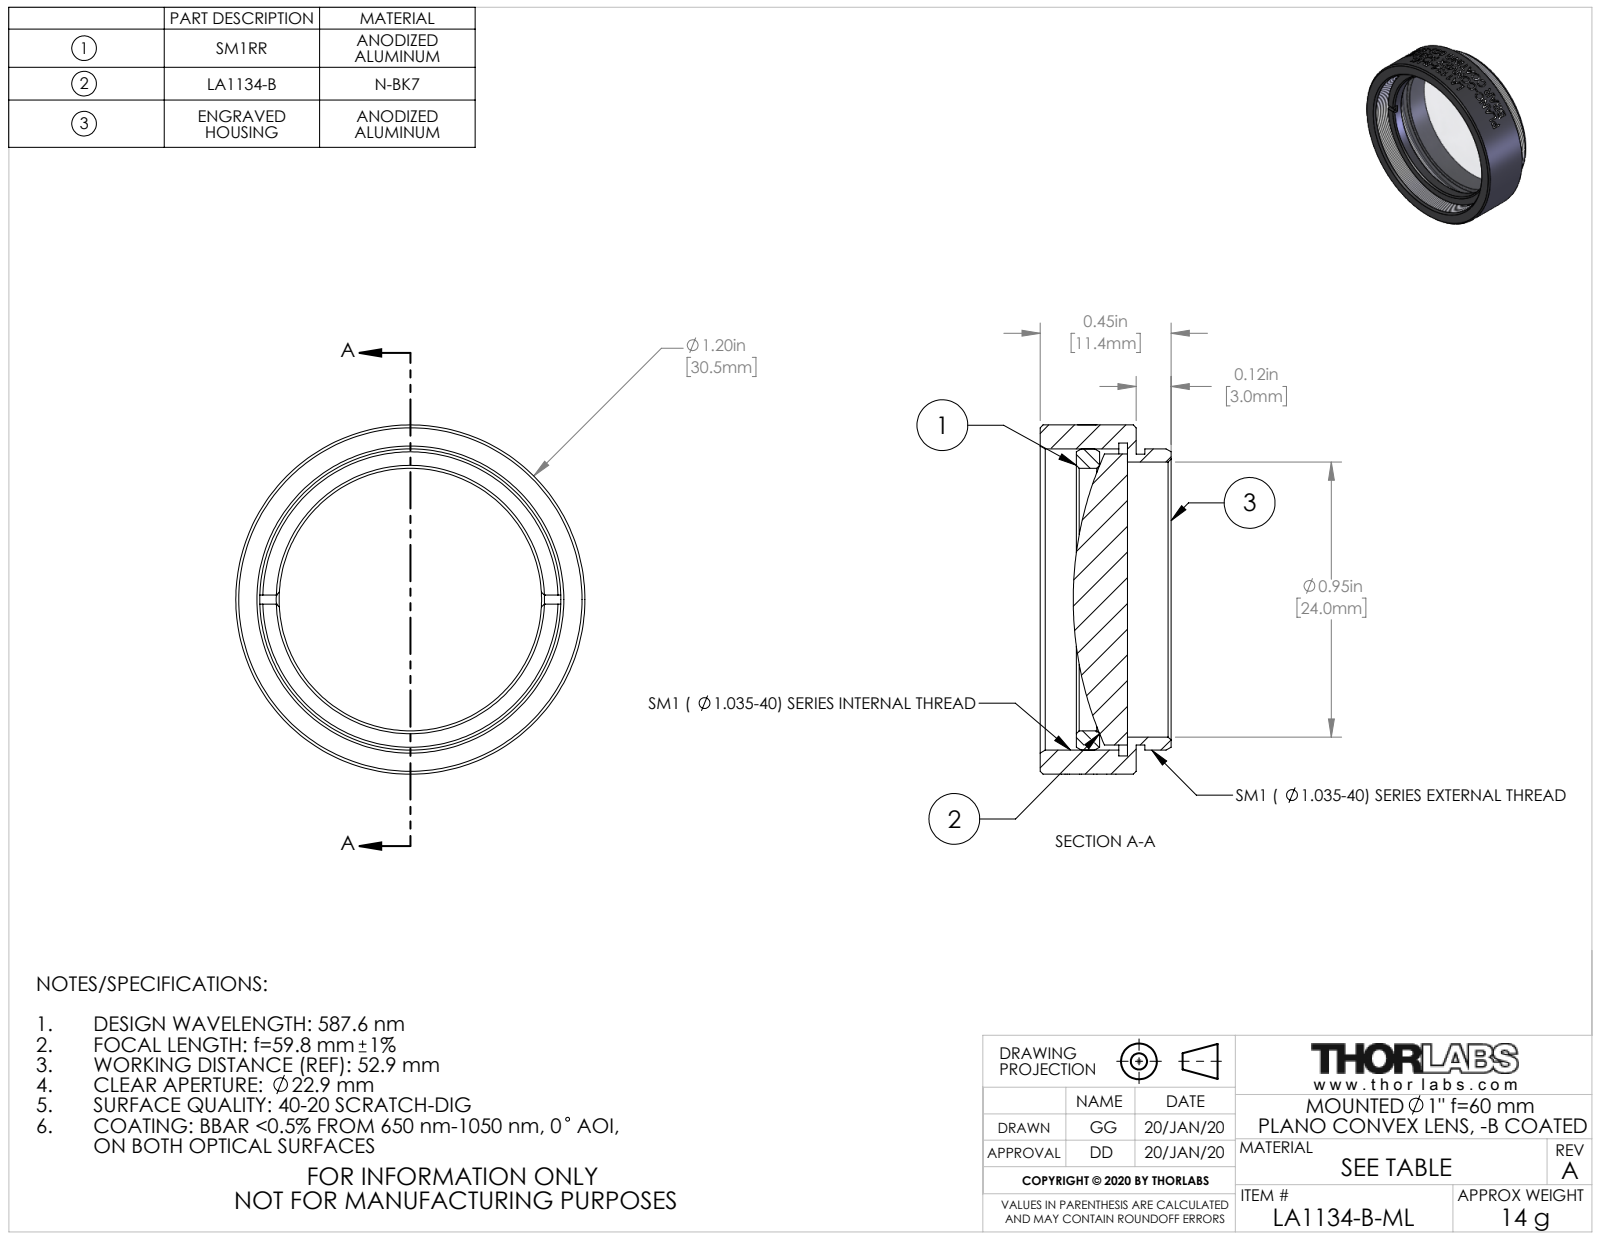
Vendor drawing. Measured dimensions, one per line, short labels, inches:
name: TTN203743-E0W
written by: SolidWorks 2018 (CONFIG_CONTROL_DESIGN)
unit: in
bodies: 3 solids, 157 faces (20 planar, 113 cylindrical, 24 other)
size: 1.2 × 1.2 × 0.45
volume: 0.232 in³; area: 6.721 in²
holes: 1× ⌀0.902, 1× ⌀0.945, 1× ⌀1.035, 1× ⌀1.075
bosses: 1× ⌀1.2, 1× ⌀1.035, 1× ⌀1, 1× ⌀0.999
face distances: 0.03, 0.33, 0.3, 0.126, 0.095, 0.205, 0.206, 0.175, 0.08, 0.125
